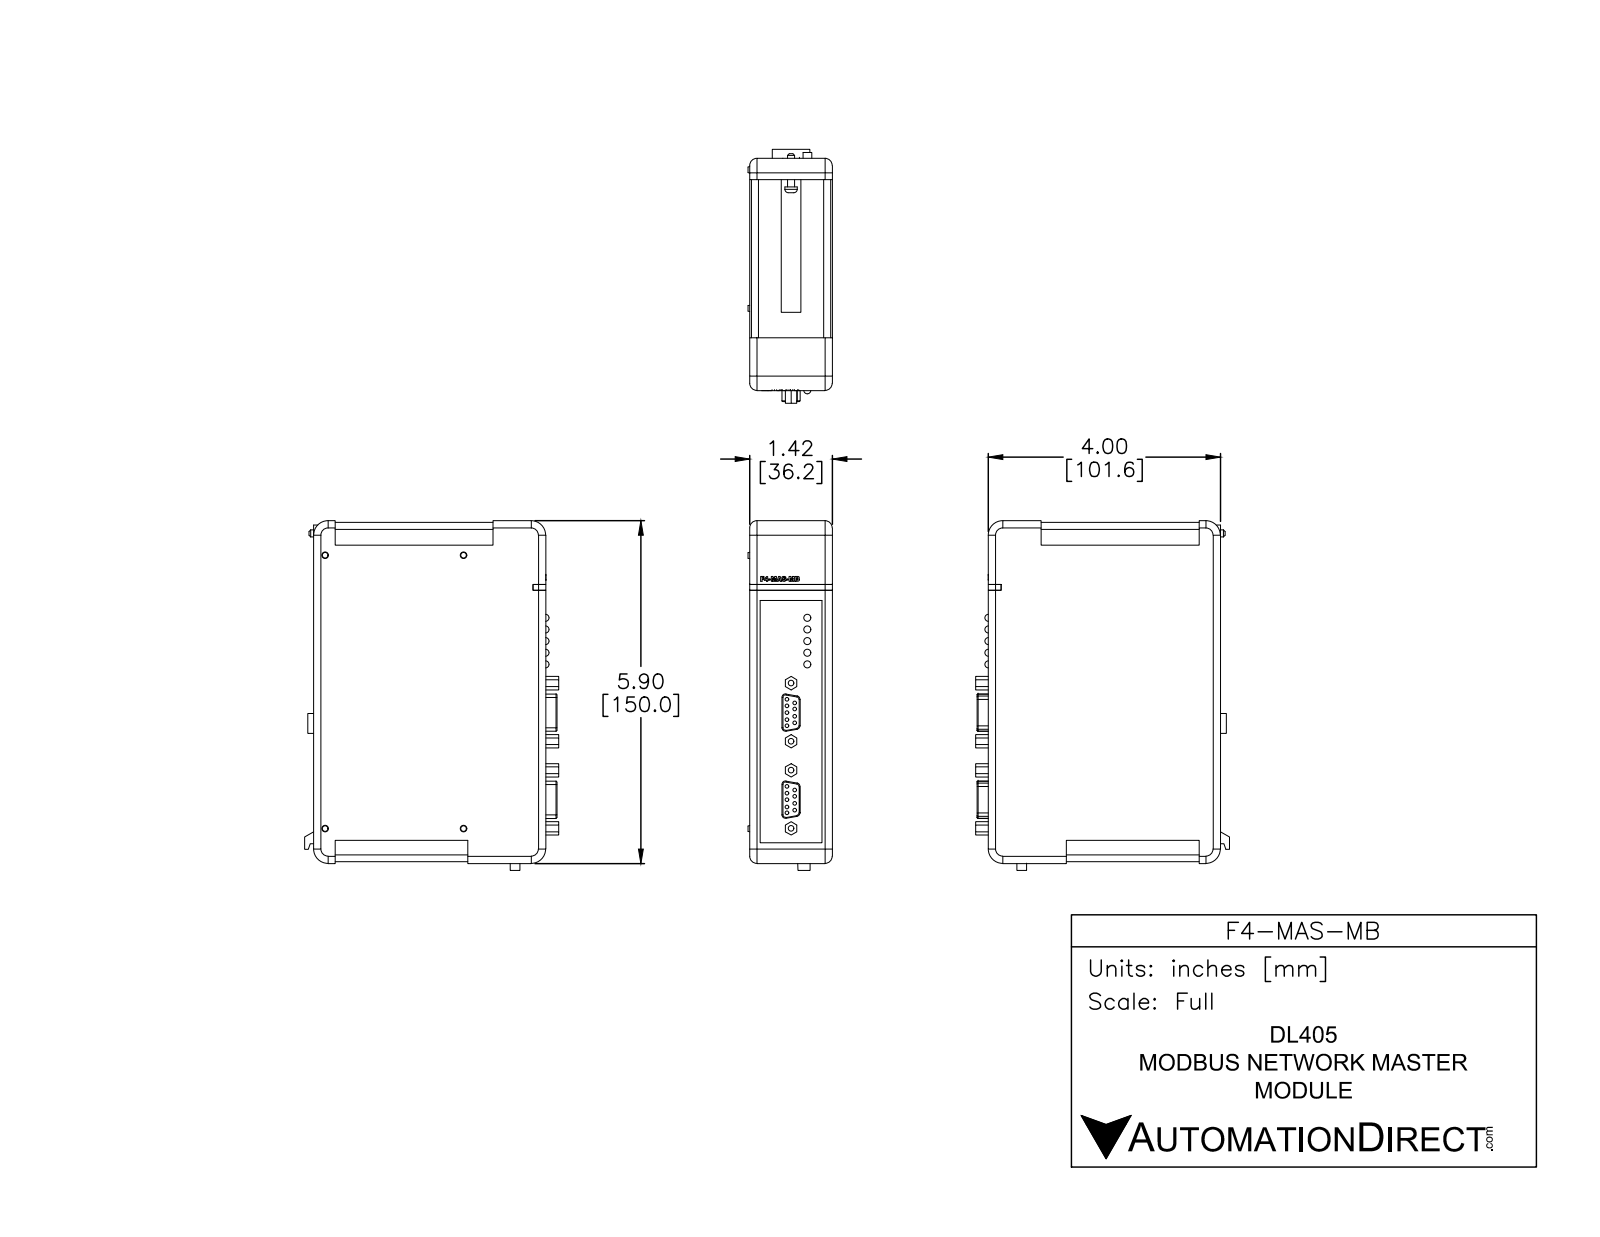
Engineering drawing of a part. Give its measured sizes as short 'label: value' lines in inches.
name: F4-MAS-MB
written by: SolidWorks 2014 (AUTOMOTIVE_DESIGN)
unit: in
bodies: 2 solids, 424 faces (243 planar, 104 cylindrical, 77 other)
size: 5.905 × 4.375 × 1.455
volume: 32.49 in³; area: 81.89 in²
holes: 10× ⌀0.065, 8× ⌀0.065, 4× ⌀0.1
bosses: 5× ⌀0.125, 1× ⌀0.212, 1× ⌀0.123
rounds: 8× R0.06, 8× R0.125, 6× R0.015, 4× R0.12, 4× R0.25, 1× R0.145, 1× R0.171
face distances: 1.425, 0.03, 3.97, 1.395, 5.875, 5.845, 4, 0.2, 3.77, 3.8
hole spacings: 1.5, 0.113, 0.125, 0.144, 0.146, 0.32, 0.322, 0.103
